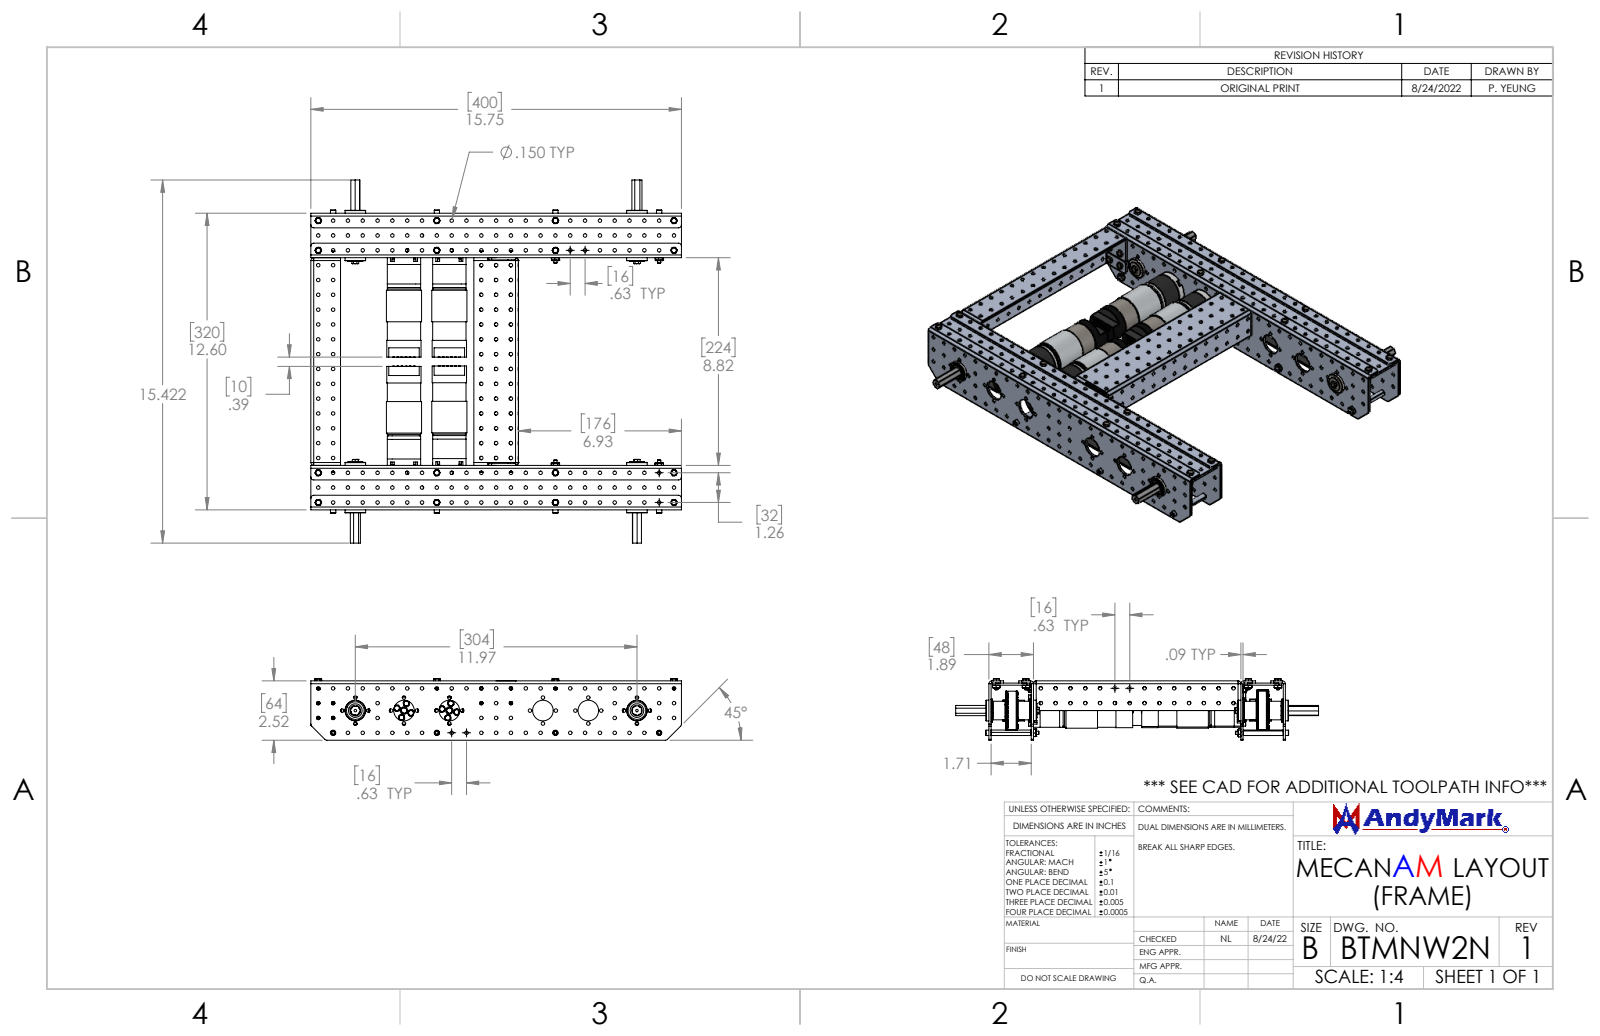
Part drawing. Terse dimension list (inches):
name: am-1658 6 x 0.625 OD 18-8 Stainless Steel Fender Washer; NeveRest Orbital 2 Stage Gearbox 6mm D; 10-32 x 0.25 Set Screw CP_91375A438; am-3947-500 375H x 500IN Spacer (+8 more)
written by: SolidWorks 2022 (AUTOMOTIVE_DESIGN)
unit: in
bodies: 356 solids, 33292 faces (5048 planar, 13216 cylindrical, 15028 other)
size: 15.748 × 15.422 × 2.613
volume: 64.57 in³; area: 1 066 in²
holes: 352× ⌀0.15, 120× ⌀0.116, 30× ⌀0.098, 28× ⌀0.111, 28× ⌀0.191, 18× ⌀0.107, 16× ⌀0.14, 14× ⌀0.125, 11× ⌀0.125, 8× ⌀0.041, 4× ⌀0.138, 4× ⌀0.157
bosses: 42× ⌀0.138, 26× ⌀0.15, 23× ⌀0.217, 23× ⌀0.118, 11× ⌀0.093, 5× ⌀1.654, 4× ⌀0.234, 4× ⌀0.226
rounds: 640× R0.01, 384× R0.012, 384× R0.017, 384× R0.017, 384× R0.054, 384× R0.069, 384× R0.089, 384× R0.112
face distances: 0.09, 1.8, 10.709, 1.89, 10.619, 8.909, 1.709, 10.799, 12.508, 0.09
hole spacings: 0.63, 1.26, 1.89, 3.15, 1.409, 1.992, 2.52, 3.78
